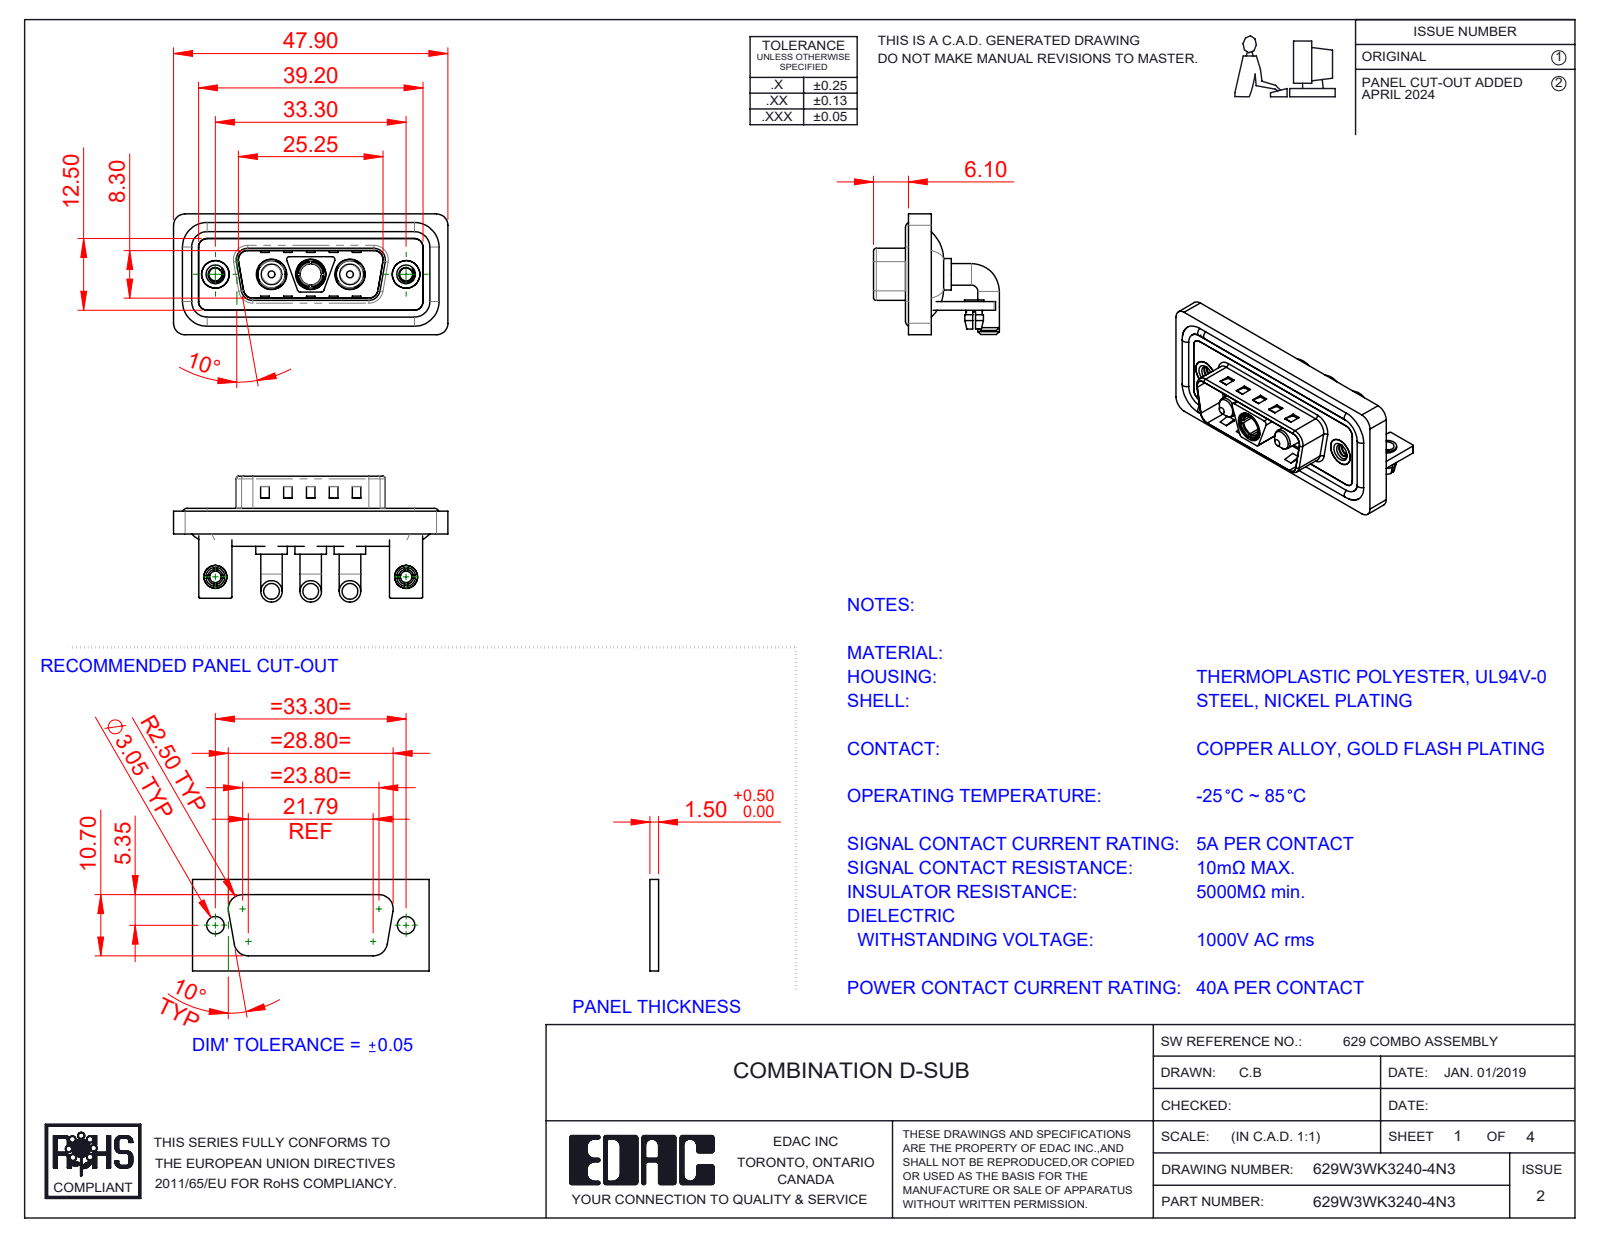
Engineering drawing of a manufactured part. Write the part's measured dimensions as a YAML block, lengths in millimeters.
part_name: "629Combo Threaded Rivet_3; Power Pin_40A RA; 629Combo Shell Front_15 Contacts; Power Socket_40A RA (+6 more)"
step_written_by: "SolidWorks 2023 (CONFIG_CONTROL_DESIGN)"
units: millimeters
bodies: {solids: 17, faces: 753, planar: 299, cylindrical: 306, other: 148}
overall_size: [47.9, 21.98, 21.1]
volume: 6421
surface_area: 10347
round_holes:
  - {diameter: 4.85, count: 3}
  - {diameter: 5.3, count: 3}
  - {diameter: 2, count: 2}
  - {diameter: 2.26, count: 2}
  - {diameter: 2.5, count: 2}
  - {diameter: 3.2, count: 2}
  - {diameter: 4, count: 2}
  - {diameter: 4.8, count: 2}
  - {diameter: 5, count: 2}
  - {diameter: 3.7, count: 1}
round_bosses_or_shafts:
  - {diameter: 3.75, count: 6}
  - {diameter: 1.6, count: 4}
  - {diameter: 5.5, count: 3}
  - {diameter: 5.2, count: 3}
  - {diameter: 4.75, count: 3}
  - {diameter: 4.9, count: 2}
  - {diameter: 4, count: 2}
  - {diameter: 3.6, count: 2}
partial_cylinders:
  - {radius: 2, count: 21}
  - {radius: 1.5, count: 18}
  - {radius: 0.25, count: 16}
  - {radius: 0.5, count: 13}
  - {radius: 1.6, count: 8}
  - {radius: 0.6, count: 4}
  - {radius: 0.65, count: 4}
  - {radius: 0.9, count: 4}
face_to_face_distances: [0.4, 1.5, 0.8, 2.9, 1.1, 2.1, 3.7, 1.6, 1.2, 4.5]
hole_center_spacings: [6.85, 9.8, 16.65, 23.5, 33.3, 13.7]
